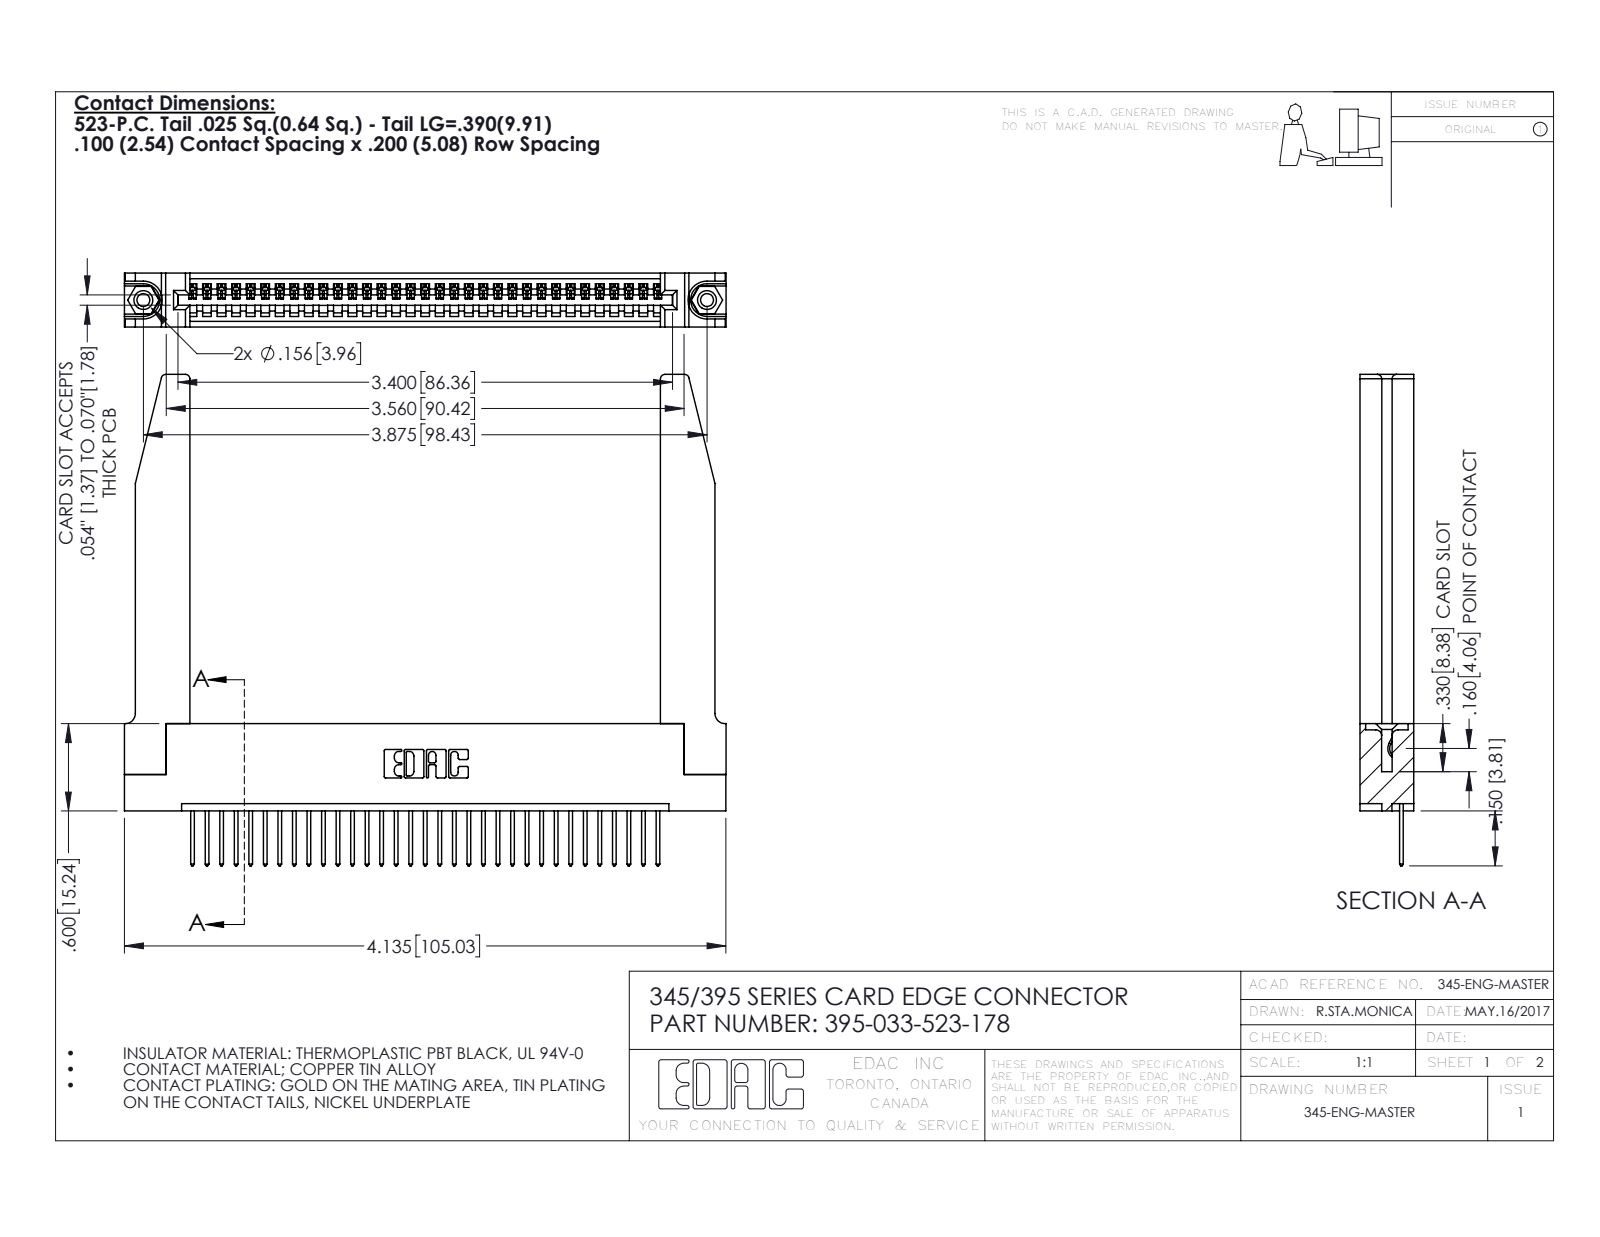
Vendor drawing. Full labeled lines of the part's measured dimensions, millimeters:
Part name (STEP PRODUCT): 345 Part_Flush Mounting Lugs - 0.156 Dia-TH; 395-033-523-178; 345-250-001_345-250-001-102; 345-220-078_345-220-078 (+1 more)
STEP written by: SolidWorks 2016 (CONFIG_CONTROL_DESIGN)
Units: millimetres
Bodies: 38 solids, 2274 faces (1542 planar, 680 cylindrical, 52 other)
Overall size (bounding box): 105.1 × 85.8 × 9.4
Volume: 17 670 mm³ · Surface area: 19 900 mm²
Round holes (diameter × count): ⌀2.3 ×2, ⌀3.2 ×2, ⌀4 ×2, ⌀1.6 ×1
Round bosses / shafts (diameter × count): ⌀3.9 ×2
Partial cylindrical surfaces — rounded edges, fillets, slot ends (radius × count): R0.2 ×66, R0.3 ×66, R0.3 ×22, R0.8 ×8, R0.2 ×6, R0.8 ×6, R0.7 ×3, R0.8 ×2
Main face-to-face distances: 9.4, 1.8, 7.6, 5.1, 2.5, 6.9, 0.6, 3.8, 3.8, 5.7
Hole centre spacings: 6.9, 92.5, 98.4
